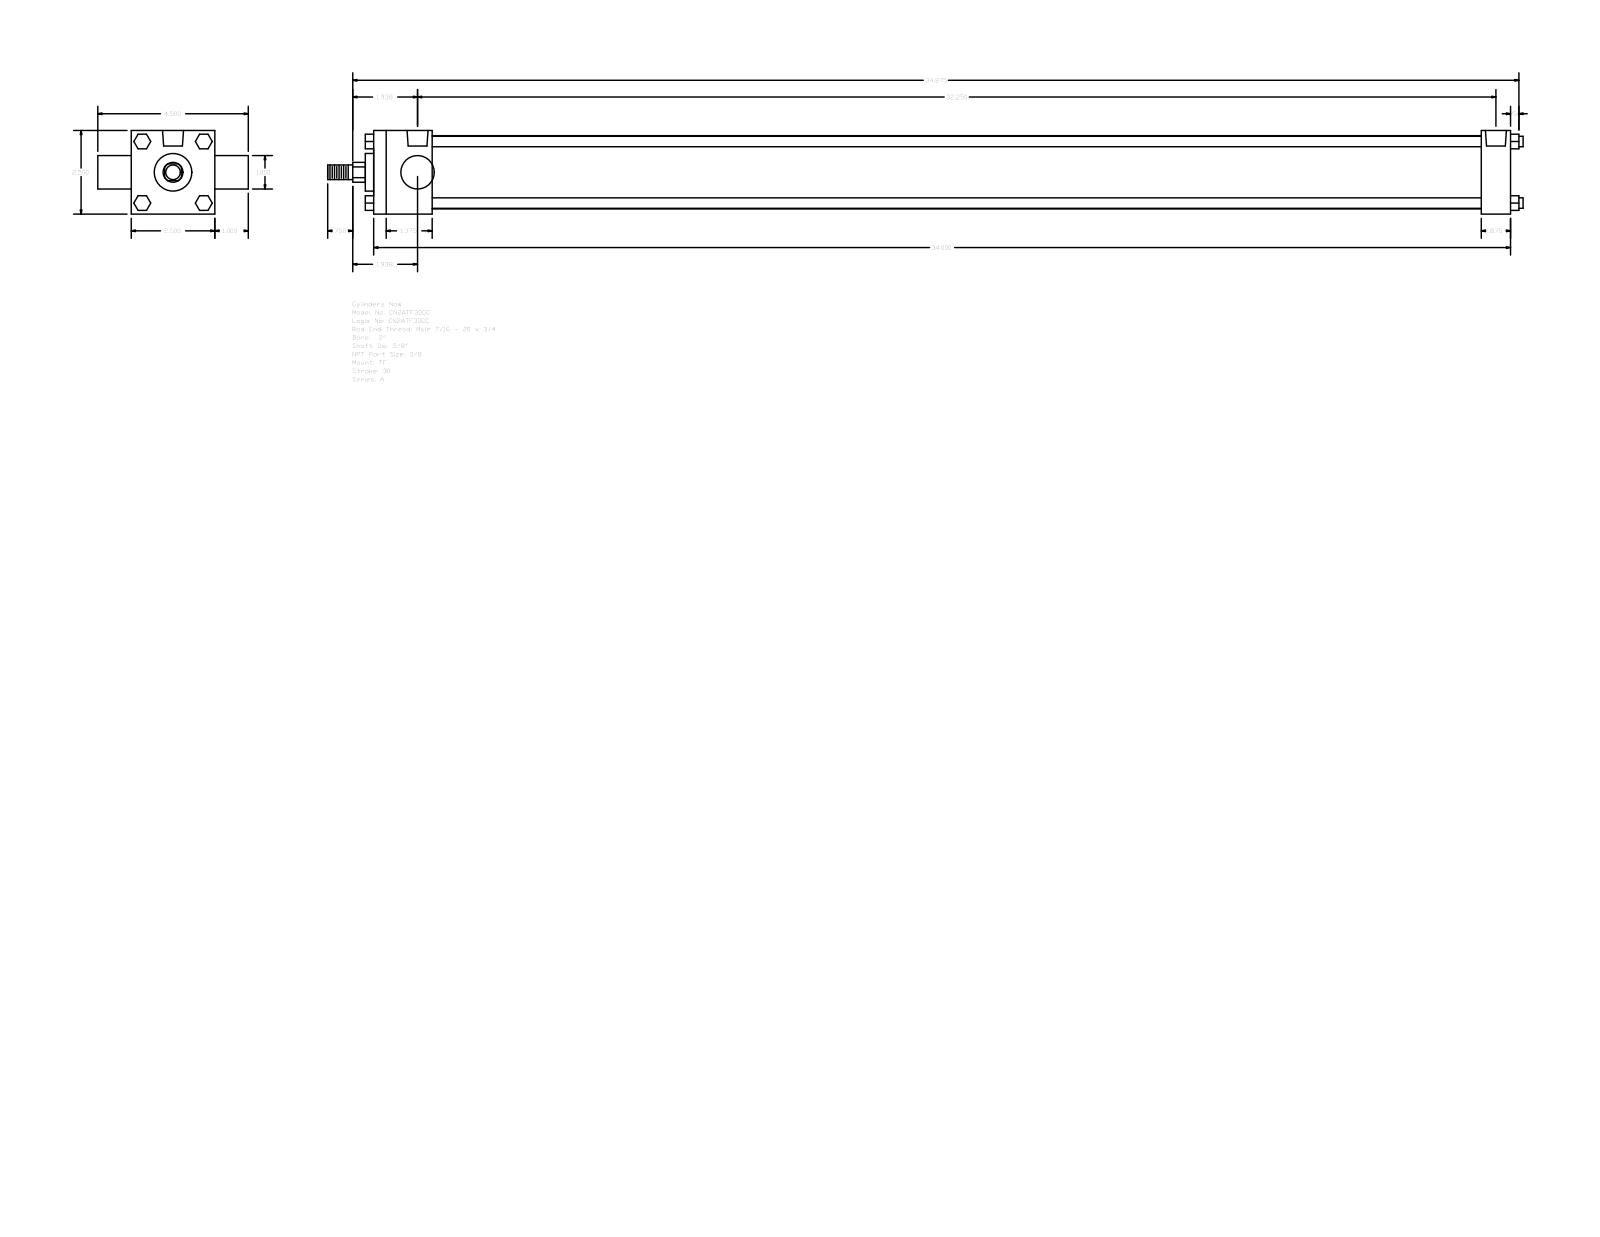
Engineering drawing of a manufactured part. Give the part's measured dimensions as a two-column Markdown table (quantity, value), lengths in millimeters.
| quantity | value |
| --- | --- |
| part name | A_TF__0200_0.625 |
| STEP written by | GSSL Pune (CONFIG_CONTROL_DESIGN) |
| units | millimeters |
| bodies | 0 solids, 120 faces (92 planar, 28 cylindrical, 0 other) |
| overall size | 908.05 × 114.3 × 63.5 |
| round holes (diameter × count) | 5.56 × 3, 15.93 × 2 |
| round bosses / shafts (diameter × count) | 7.94 × 4, 55.63 × 1, 28.57 × 1, 25.4 × 1, 15.88 × 1, 11.11 × 1 |
| partial cylindrical surfaces (radius × count) | 7.54 × 1 |
| main face-to-face distances | 63.5, 863.6, 44.45, 841.37, 796.92, 819.15, 22.23, 25.4, 88.9, 6.35 |
| hole center spacings | 3.97, 3.98, 811.2, 815.17, 815.18, 819.15 |
